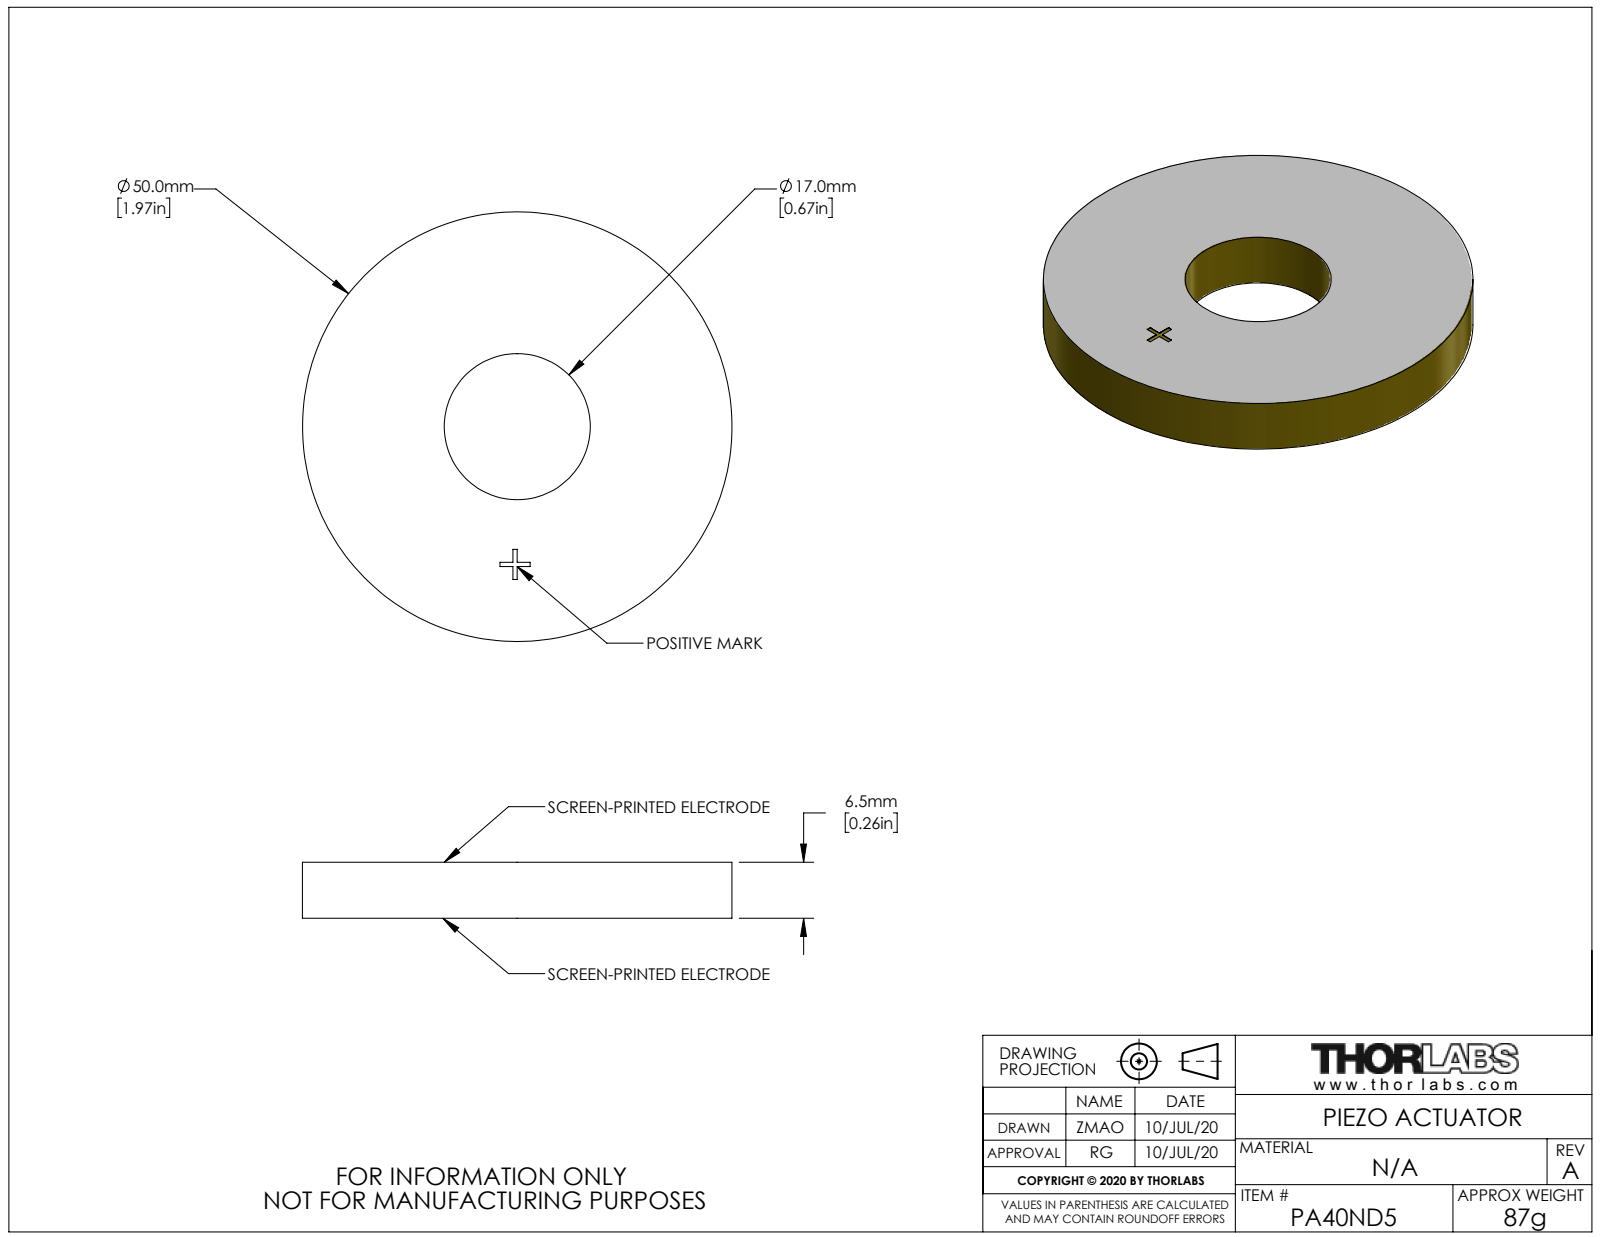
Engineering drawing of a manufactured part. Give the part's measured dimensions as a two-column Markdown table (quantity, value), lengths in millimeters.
| quantity | value |
| --- | --- |
| part name | CTN016246-E0W |
| STEP written by | SolidWorks 2018 (AUTOMOTIVE_DESIGN) |
| units | millimeters |
| bodies | 1 solid, 19 faces (15 planar, 4 cylindrical, 0 other) |
| overall size | 50 × 50 × 6.5 |
| volume | 11 287 mm³ |
| surface area | 4 841 mm² |
| round holes (diameter × count) | 17 × 1 |
| round bosses / shafts (diameter × count) | 50 × 1 |
| main face-to-face distances | 6.5, 6.49, 0.5, 1.5, 2, 3.5 |
